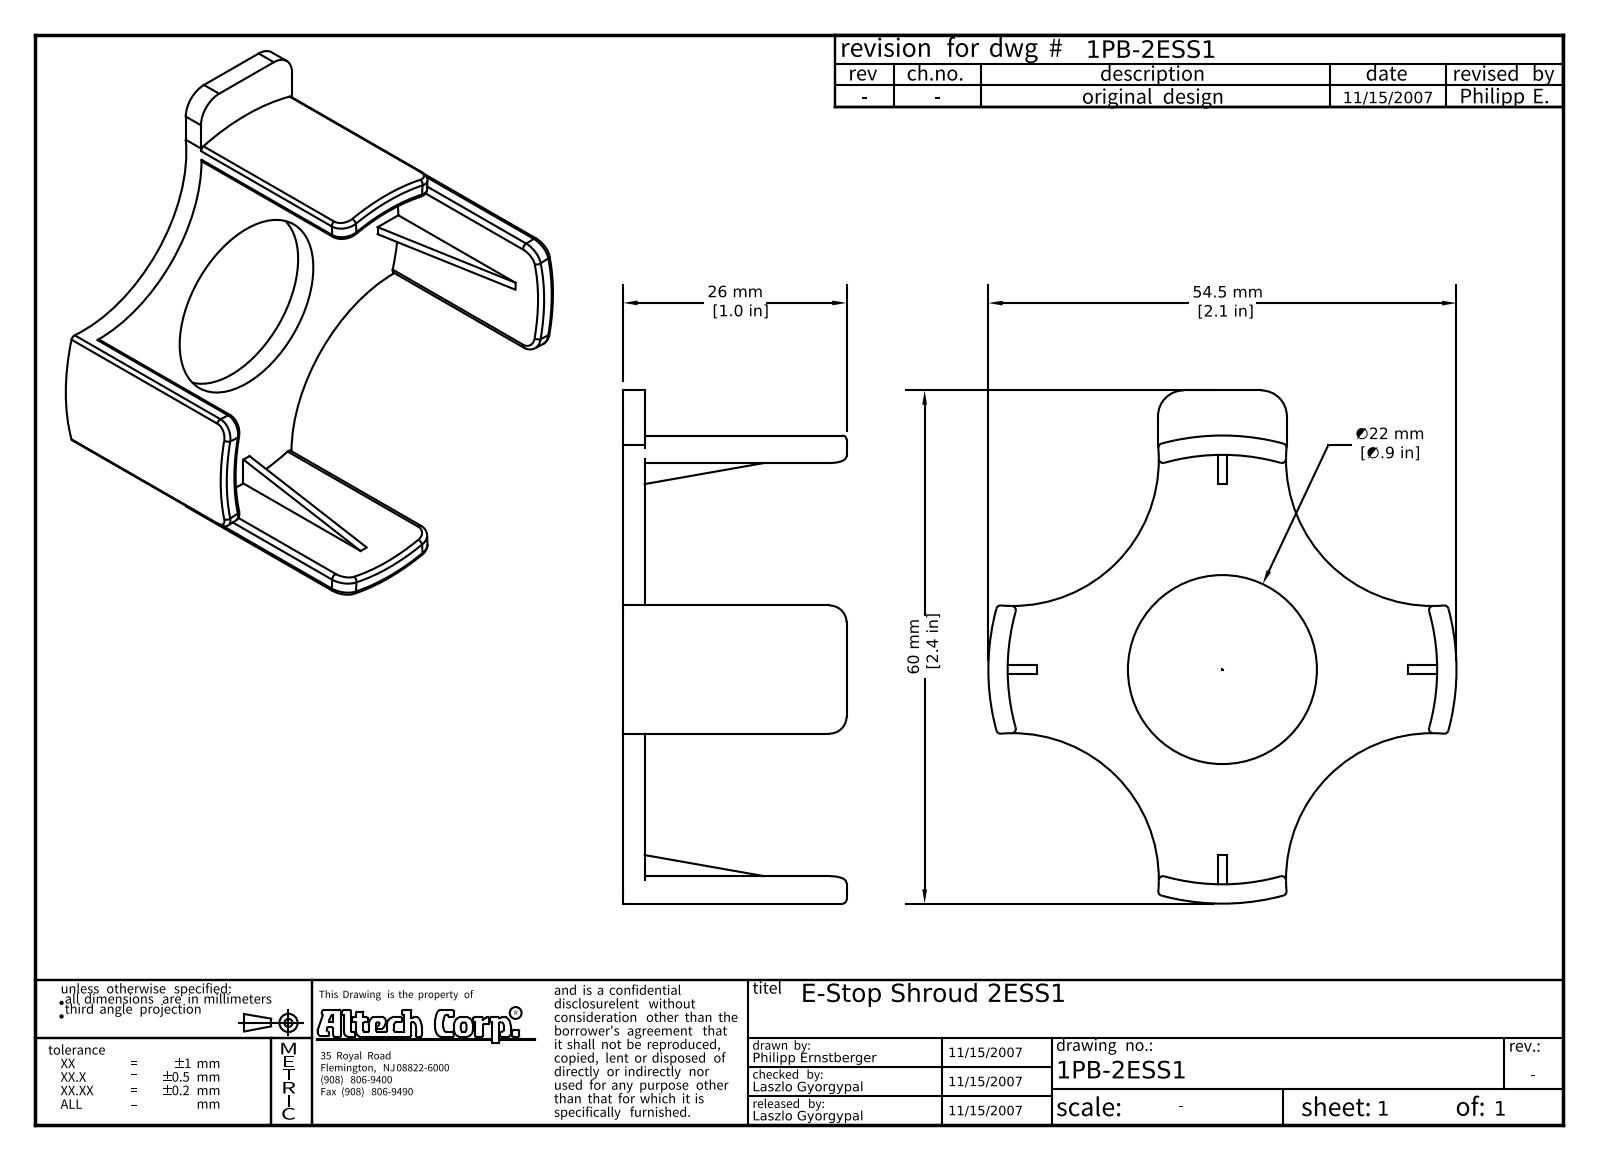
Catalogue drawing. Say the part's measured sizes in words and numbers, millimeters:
The part is named "2ESS1". Its 3-D file was written by "Autodesk Inventor 2008 (AUTOMOTIVE_DESIGN)". It is 1 solid with 85 faces: 22 planar, 31 cylindrical and 32 other. Overall it measures 59.75 by 54.5 by 26 millimeters. Its volume is 6 579 cubic millimeters and its surface area 6 670 square millimeters. Round holes: 1 of diameter 22. Partial cylindrical surfaces (rounded edges, fillets, slot ends): 16 of radius 0.5, 4 of radius 17, 2 of radius 3, 1 of radius 25, 1 of radius 27.25. The main face-to-face distances are 2.5, 1, 26, 23.5, 33, 32, 7, 8, 15.
